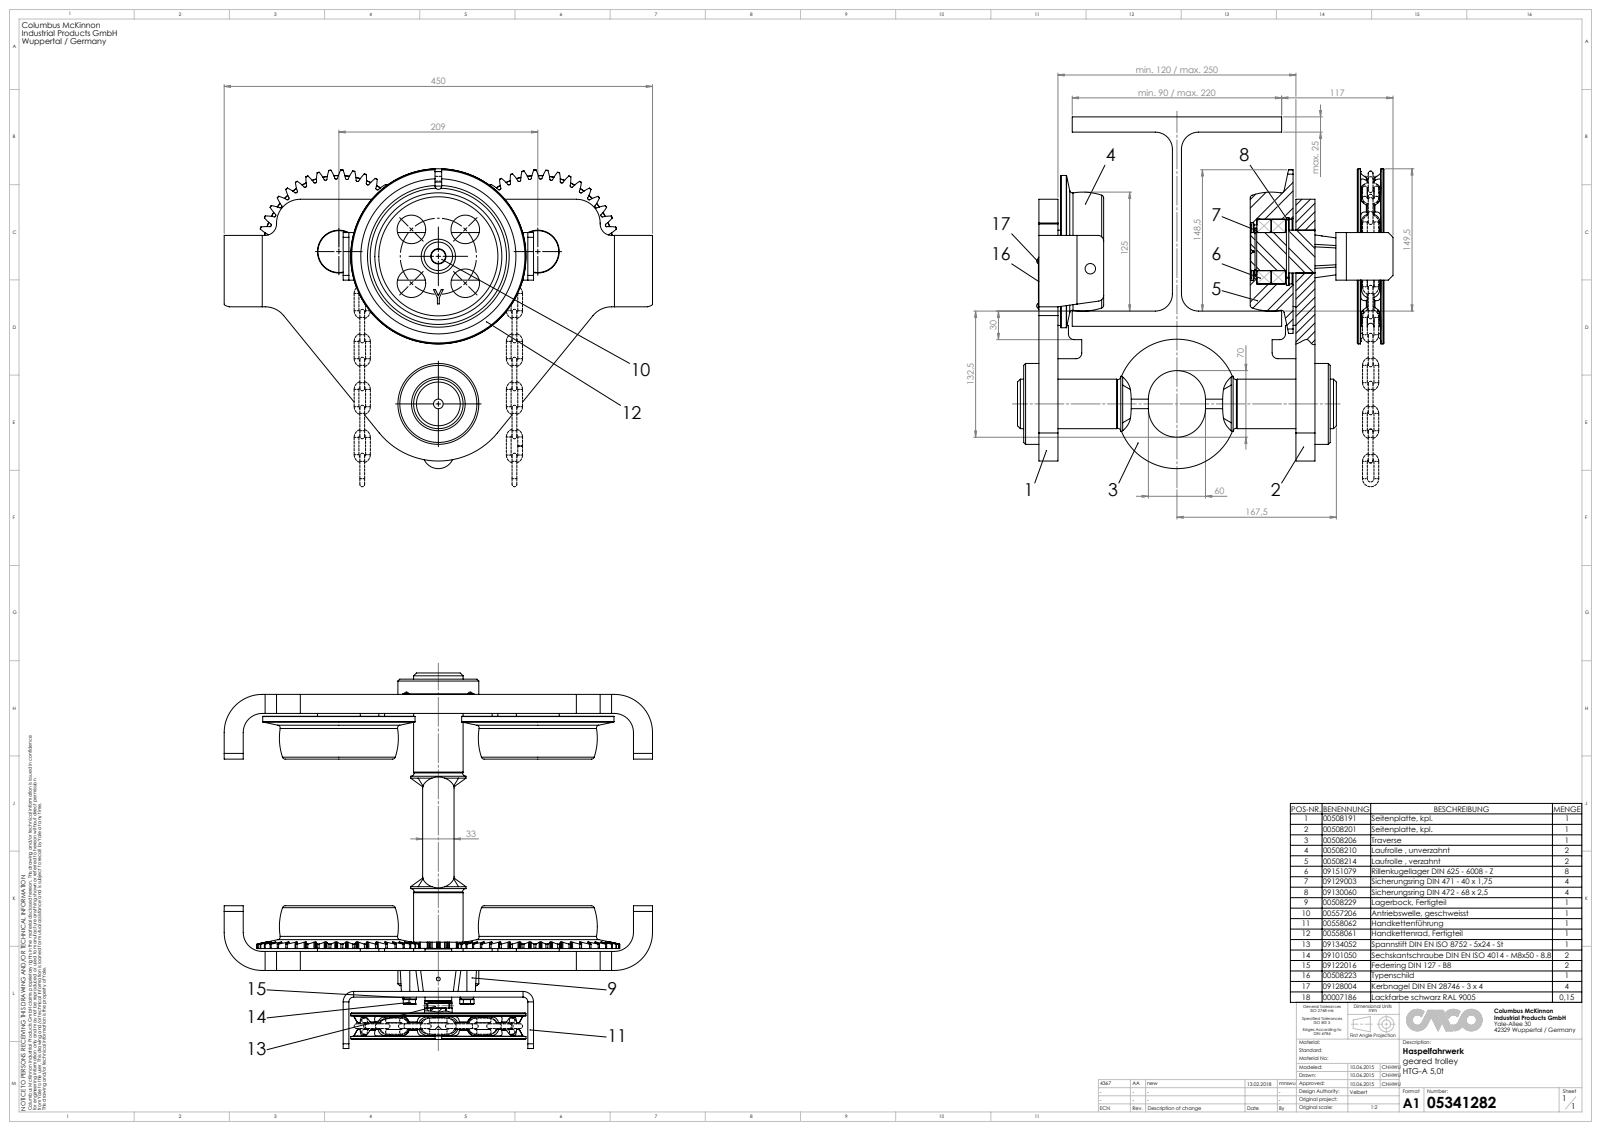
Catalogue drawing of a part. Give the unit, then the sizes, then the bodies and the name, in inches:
Units: inches
Overall size (bounding box): 19.685 × 15.531 × 15.296
Round holes (diameter × count): ⌀0.118 ×11, ⌀0.098 ×8, ⌀0.138 ×4, ⌀1.181 ×4, ⌀0.079 ×2, ⌀0.197 ×2, ⌀0.268 ×2, ⌀0.319 ×2, ⌀0.354 ×2, ⌀0.433 ×2, ⌀1.476 ×2, ⌀1.575 ×2
Round bosses / shafts (diameter × count): ⌀0.197 ×26, ⌀0.205 ×4, ⌀6.299 ×2, ⌀2.795 ×2, ⌀1.948 ×2, ⌀0.555 ×2, ⌀0.315 ×2, ⌀7.244 ×1
Partial cylindrical surfaces — rounded edges, fillets, slot ends (radius × count): R0.039 ×194, R1.575 ×176, R0.059 ×80, R0.394 ×22, R0.098 ×8, R0.236 ×8, R0.118 ×6, R0.709 ×4
Main face-to-face distances: 0.63, 8.031, 5.522, 5.896, 0.787, 10.63, 4.734, 5.108, 8.661, 7.402
Hole centre spacings: 8.228, 1.244, 0.246, 0.389, 0.473, 0.856, 0.856, 1.211
Volume: 699.9 in³ · Surface area: 2 737 in²
Bodies: 78 solids, 2568 faces (487 planar, 1266 cylindrical, 815 other)
Part name (STEP PRODUCT): HTG-A 5,0t
STEP written by: SolidWorks 2015 (AUTOMOTIVE_DESIGN)
